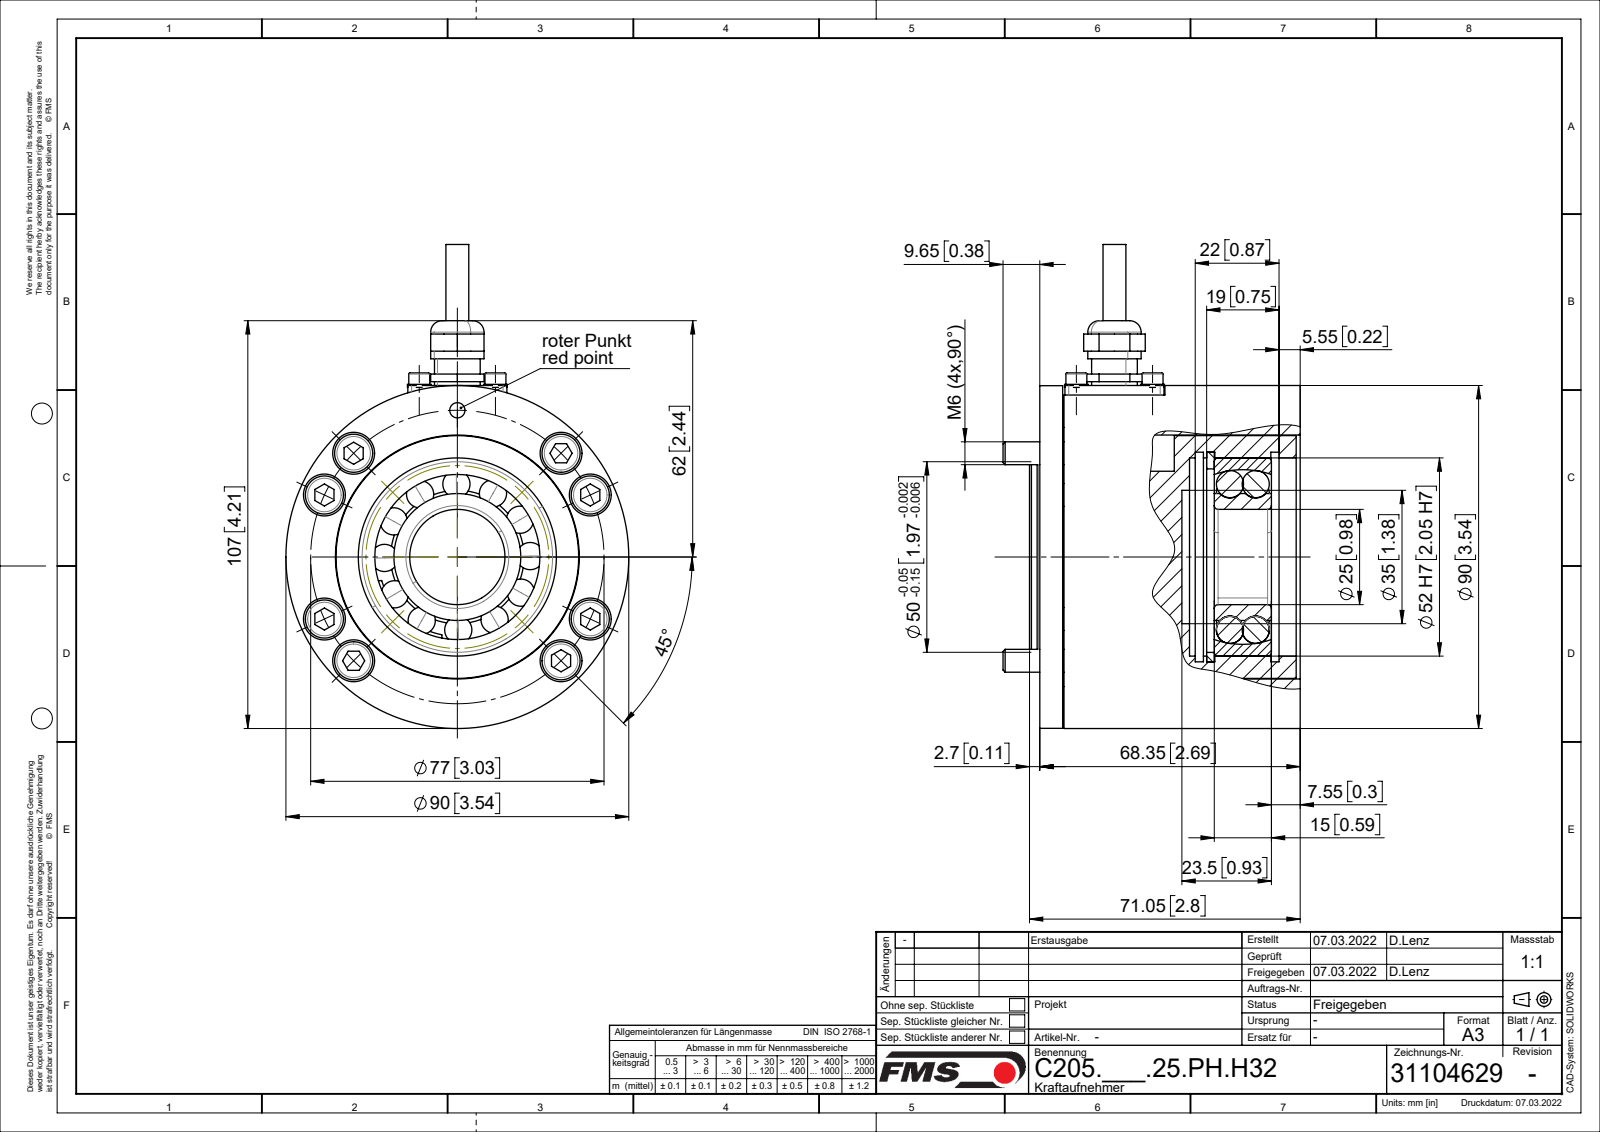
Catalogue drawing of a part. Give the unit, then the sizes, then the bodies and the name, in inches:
Units: inches
Overall size (bounding box): 5 × 3.543 × 3.071
Round holes (diameter × count): ⌀0.256 ×8, ⌀0.433 ×8, ⌀0.098 ×6, ⌀0.122 ×4, ⌀0.134 ×4, ⌀0.197 ×4, ⌀0.276 ×4, ⌀0.157 ×2, ⌀0.236 ×1, ⌀0.402 ×1, ⌀0.48 ×1, ⌀0.709 ×1
Round bosses / shafts (diameter × count): ⌀0.394 ×8, ⌀0.236 ×8, ⌀0.244 ×4, ⌀0.217 ×4, ⌀0.118 ×4, ⌀3.543 ×1, ⌀3.539 ×1, ⌀2.508 ×1
Partial cylindrical surfaces — rounded edges, fillets, slot ends (radius × count): R0.004 ×4, R0.039 ×4, R0.167 ×2, R0.197 ×2, R0.819 ×1, R0.949 ×1
Main face-to-face distances: 0.236, 0.13, 0.106, 0.256, 1.26, 1.301, 0.079, 1.496, 1.154, 1.39
Hole centre spacings: 0.787, 1.516, 0.526, 0.557, 1.515, 1.739, 2.143, 2.483
Volume: 18.23 in³ · Surface area: 187.6 in²
Bodies: 49 solids, 608 faces (222 planar, 234 cylindrical, 152 other)
Part name (STEP PRODUCT): Zyl-Schr DIN912_M3x6; Zyl-Schr DIN912_M6x30; 31104502_01; Federringe_DIN127A_M03 (+8 more)
STEP written by: SolidWorks 2018 (CONFIG_CONTROL_DESIGN)
